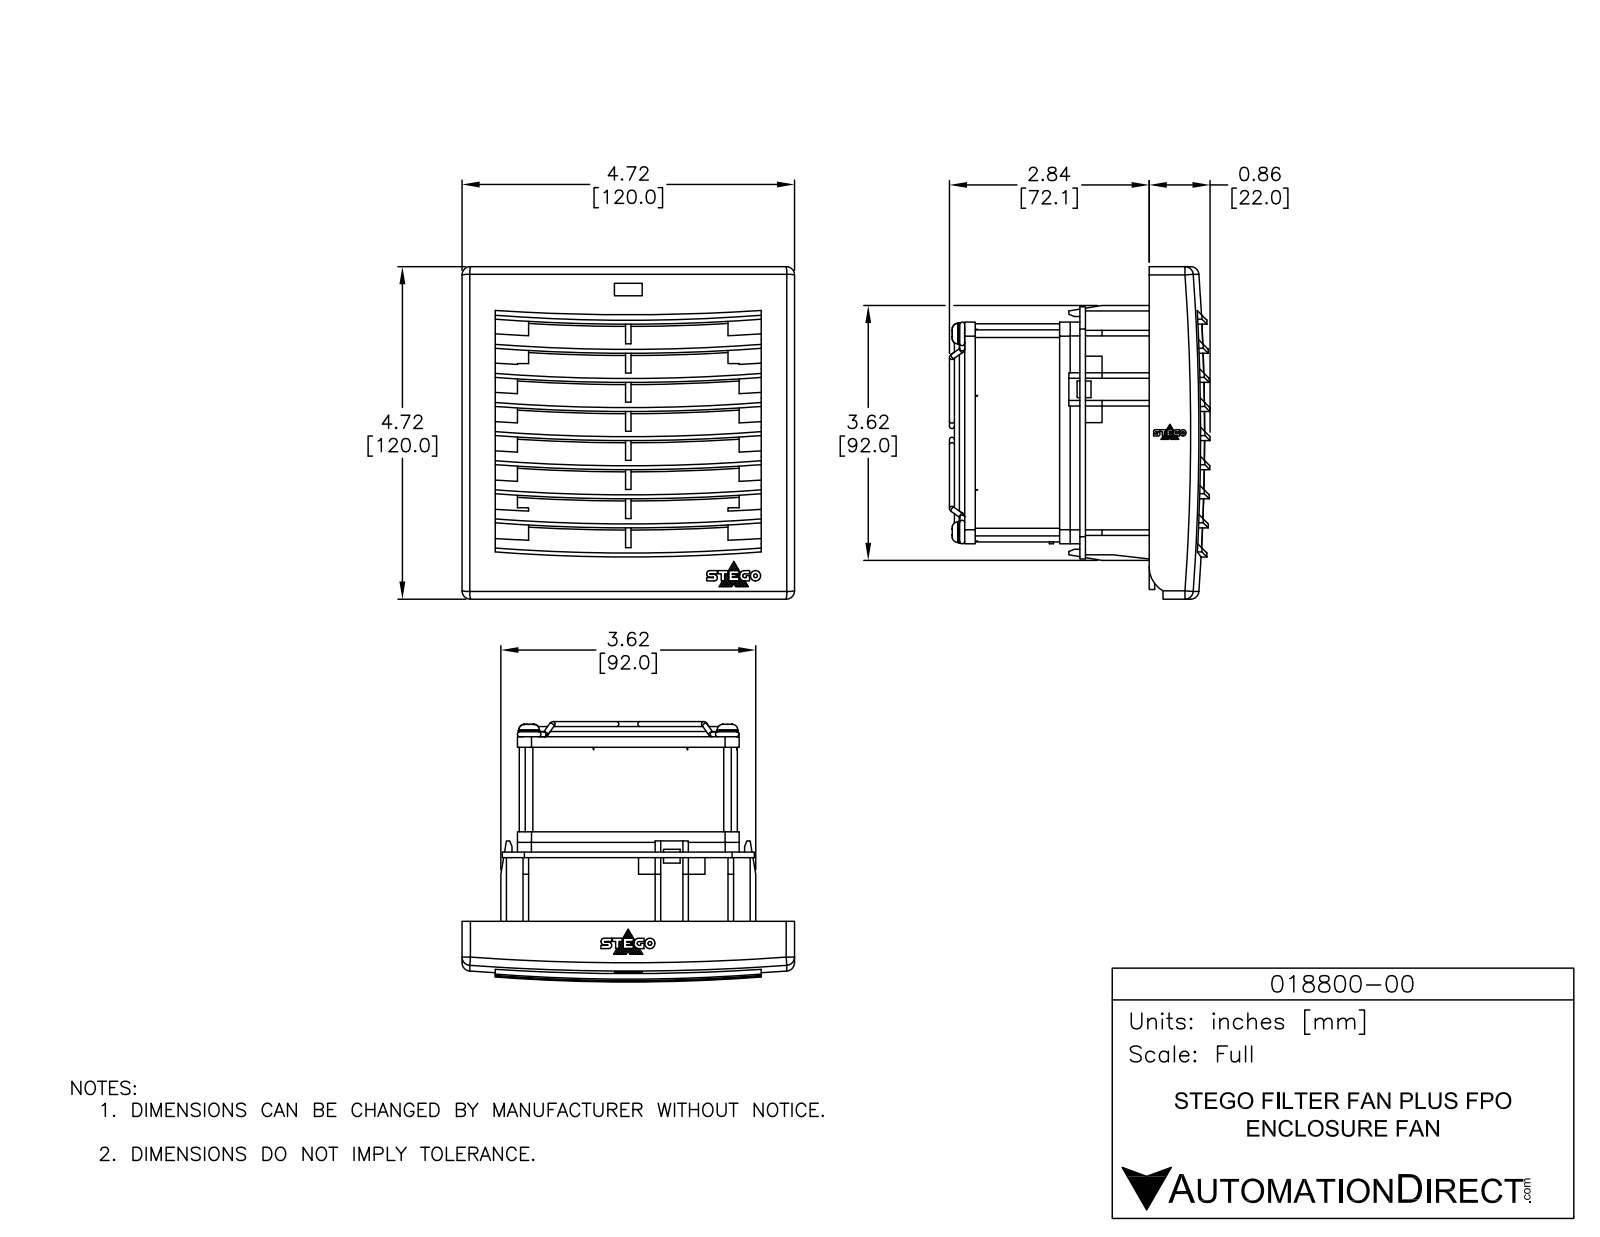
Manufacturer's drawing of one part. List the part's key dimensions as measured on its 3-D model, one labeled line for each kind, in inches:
Part name (STEP PRODUCT): 018800-00
STEP written by: SolidWorks 2018 (AUTOMOTIVE_DESIGN)
Units: inches
Bodies: 1 solid, 506 faces (293 planar, 205 cylindrical, 8 other)
Overall size (bounding box): 4.724 × 4.724 × 3.74
Volume: 20.27 in³ · Surface area: 222.5 in²
Round holes (diameter × count): ⌀0.217 ×4, ⌀0.671 ×1, ⌀1.153 ×1, ⌀1.635 ×1, ⌀1.996 ×1, ⌀2.117 ×1, ⌀2.496 ×1, ⌀2.677 ×1, ⌀3.079 ×1
Round bosses / shafts (diameter × count): ⌀2.661 ×1, ⌀2.274 ×1, ⌀2.161 ×1, ⌀1.792 ×1, ⌀1.31 ×1, ⌀0.937 ×1, ⌀0.828 ×1
Partial cylindrical surfaces — rounded edges, fillets, slot ends (radius × count): R8.63 ×15, R1.312 ×5, R0.1 ×4, R0.118 ×4, R0.539 ×1, R0.748 ×1, R0.83 ×1, R1.715 ×1
Main face-to-face distances: 0.059, 0.316, 0.12, 0.091, 3.531, 0.632, 0.239, 0.375, 0.551, 0.642
Hole centre spacings: 2.082, 2.945, 4.165
